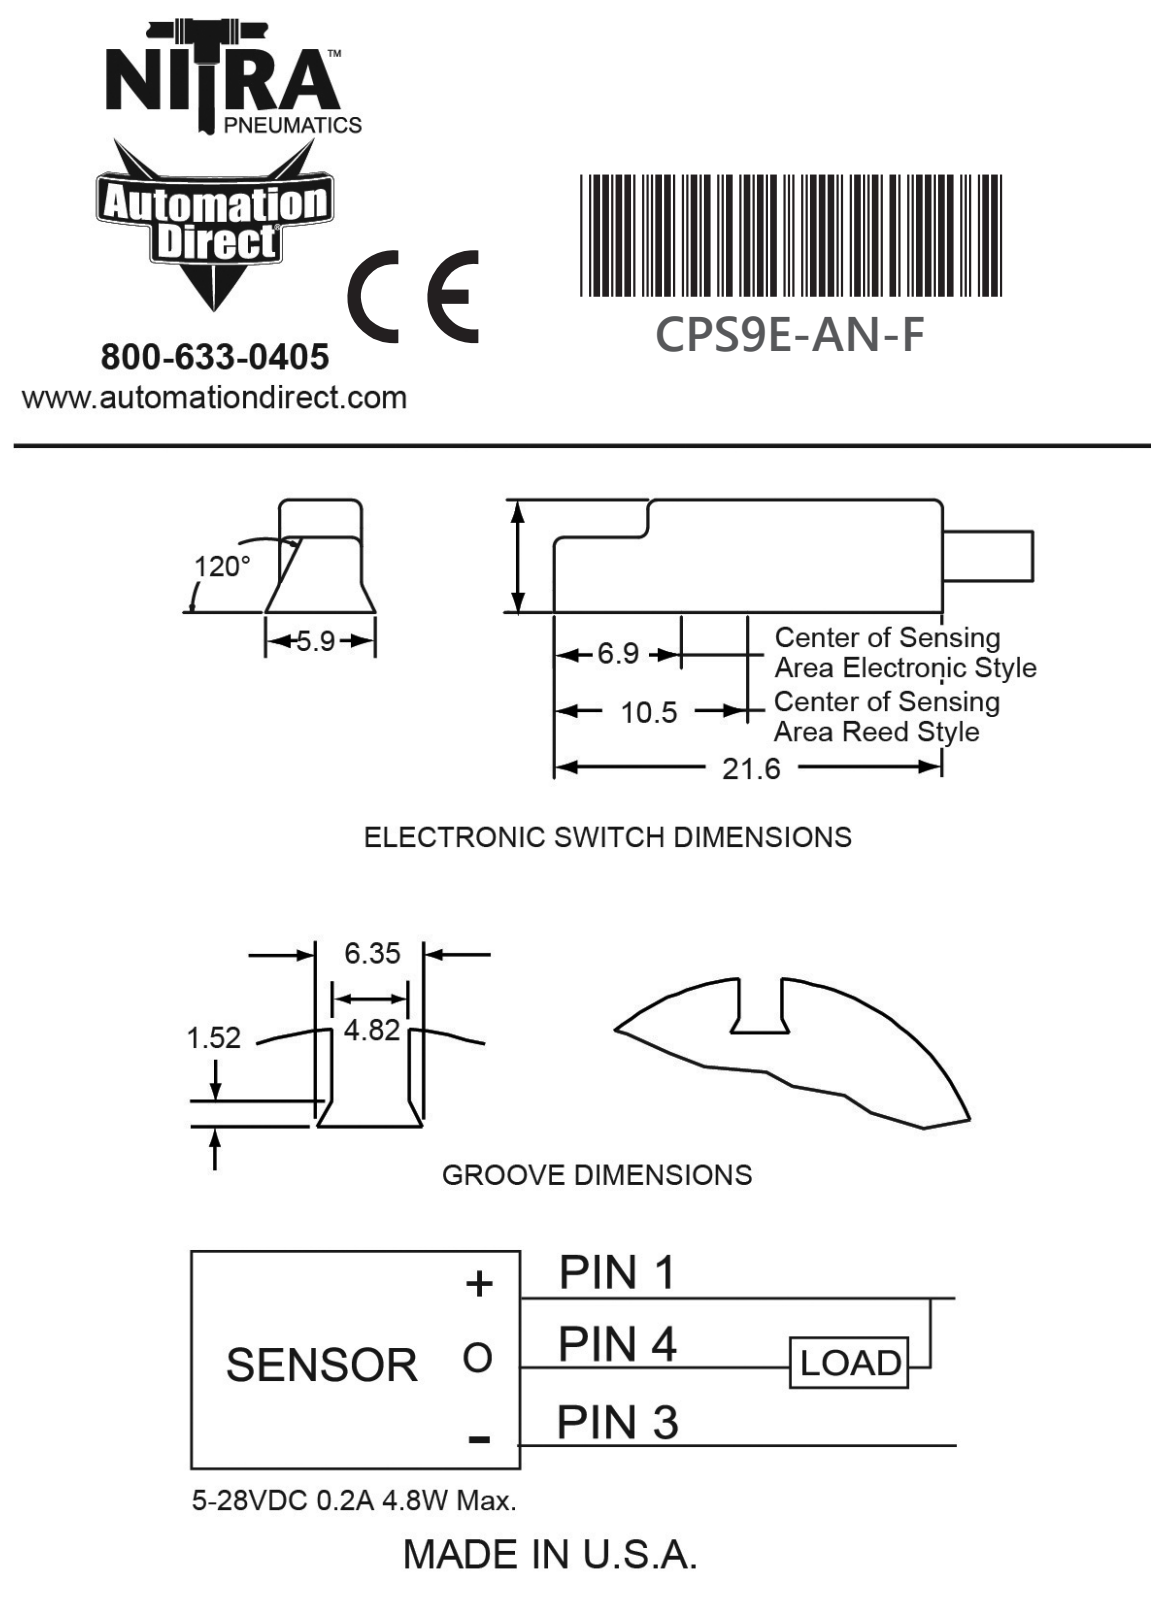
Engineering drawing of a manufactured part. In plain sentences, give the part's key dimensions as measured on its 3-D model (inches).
The part is named "CPS9E-AN-F". Its 3-D file was written by "SolidWorks 2023 (CONFIG_CONTROL_DESIGN)". It is 1 solid with 263 faces: 89 planar, 118 cylindrical and 56 other. Overall it measures 7.78 by 0.33 by 0.33 inches. Its volume is 0.162 cubic inches and its surface area 4.79 square inches. Round holes: 3 of diameter 0.039, 3 of diameter 0.049, 1 of diameter 0.094, 1 of diameter 0.125. Round bosses or shafts: 3 of diameter 0.044, 3 of diameter 0.039, 1 of diameter 0.33, 1 of diameter 0.31, 1 of diameter 0.309, 1 of diameter 0.3, 1 of diameter 0.276, 1 of diameter 0.256. Partial cylindrical surfaces (rounded edges, fillets, slot ends): 20 of radius 0.02. The main face-to-face distances are 0.02, 0.1, 0.08, 0.04, 0.06, 0.12, 0.04, 0.06, 0.175, 0.14. The hole center spacings are 0.097, 0.138, 0.172.
